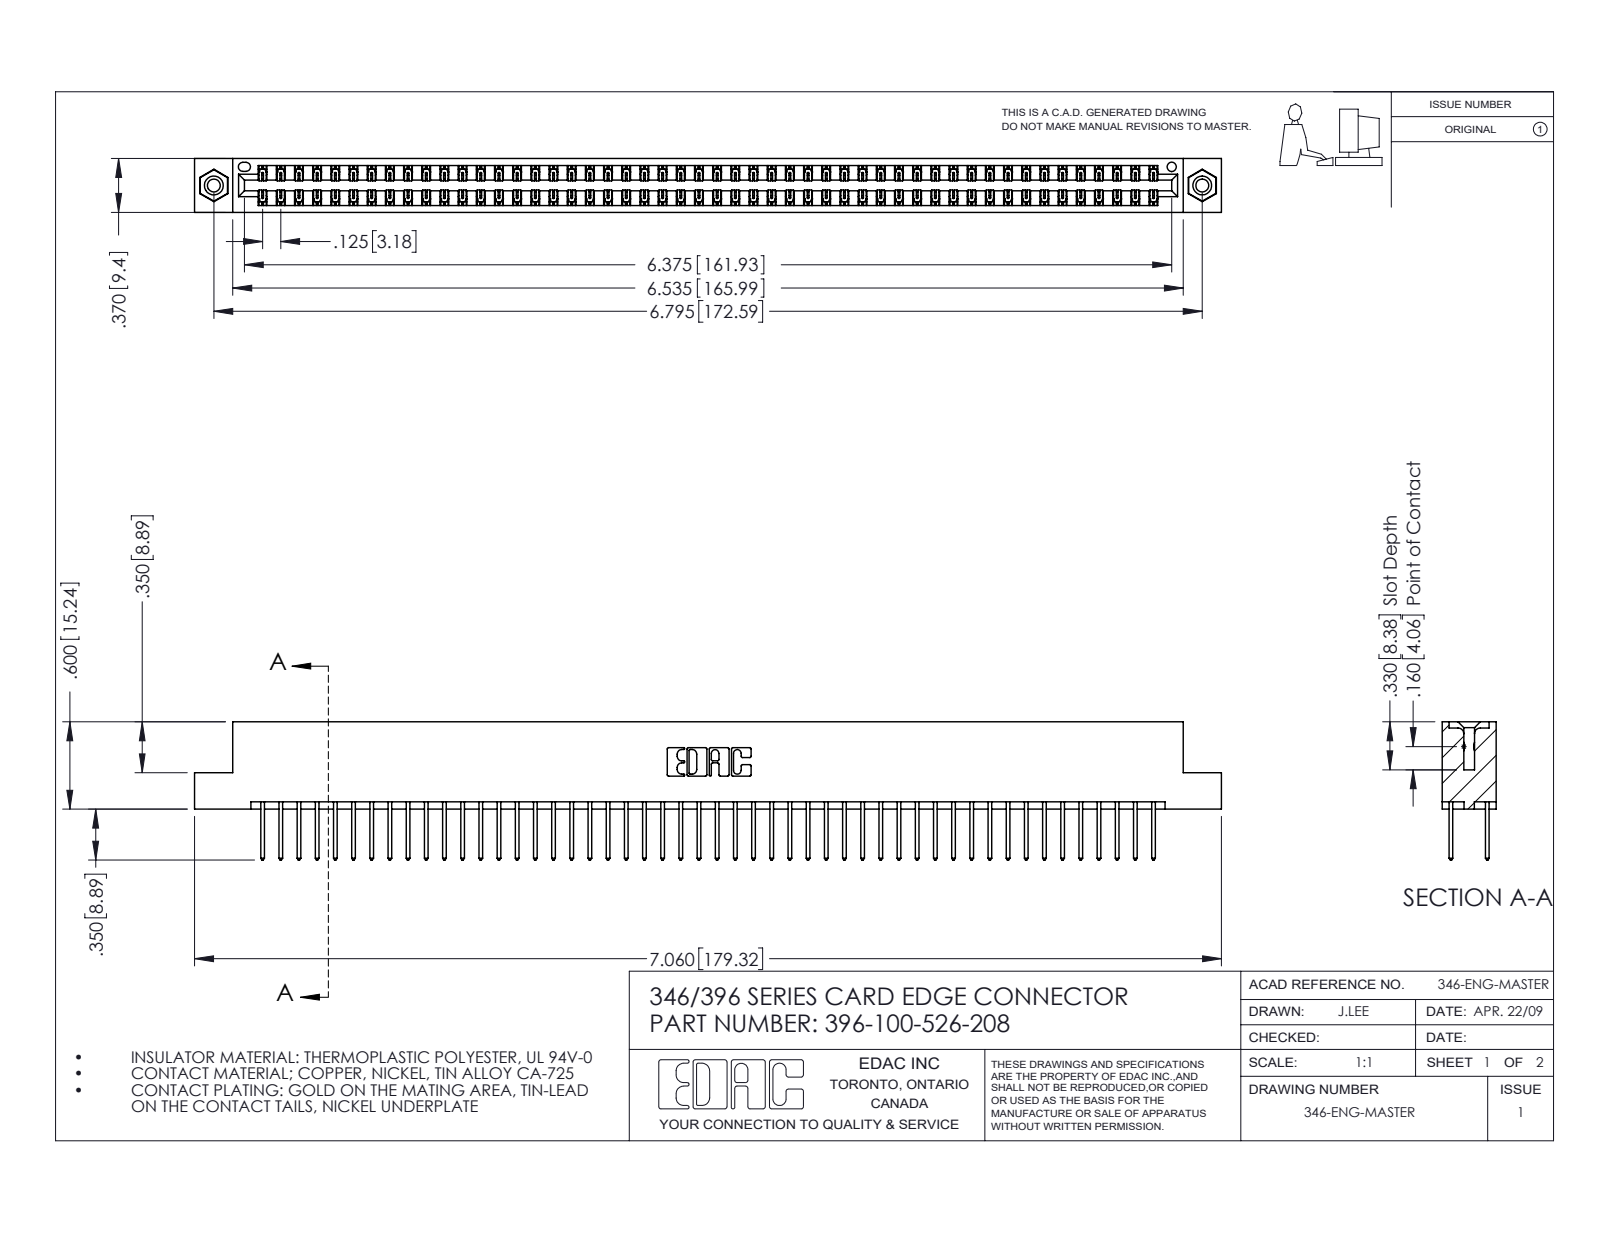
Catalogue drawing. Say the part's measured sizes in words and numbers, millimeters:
The part is named "346 Part_Flush Mounting Lugs - 0.156 Dia-TI; 345-292-001_345-293-126; 396-100-526-208; 345-250-001_345-250-003-102". Its 3-D file was written by "SolidWorks 2016 (CONFIG_CONTROL_DESIGN)". It is 103 solids with 5382 faces: 3608 planar, 1758 cylindrical and 16 other. Overall it measures 179.3 by 24.1 by 9.4 millimeters. Its volume is 17 700 cubic millimeters and its surface area 25 220 square millimeters. Round holes: 2 of diameter 2.3, 2 of diameter 3.2, 2 of diameter 4, 1 of diameter 1.6. Round bosses or shafts: 2 of diameter 3.9. Partial cylindrical surfaces (rounded edges, fillets, slot ends): 150 of radius 0.2, 100 of radius 0.3, 22 of radius 0.3, 6 of radius 0.2, 6 of radius 0.8, 3 of radius 0.7, 2 of radius 0.4, 2 of radius 0.6. The main face-to-face distances are 1.2, 8.2, 6.4, 9.4, 1.8, 7.6, 0.6, 7, 3.8, 5.6. The hole center spacings are 6.2, 167.3, 172.6.
